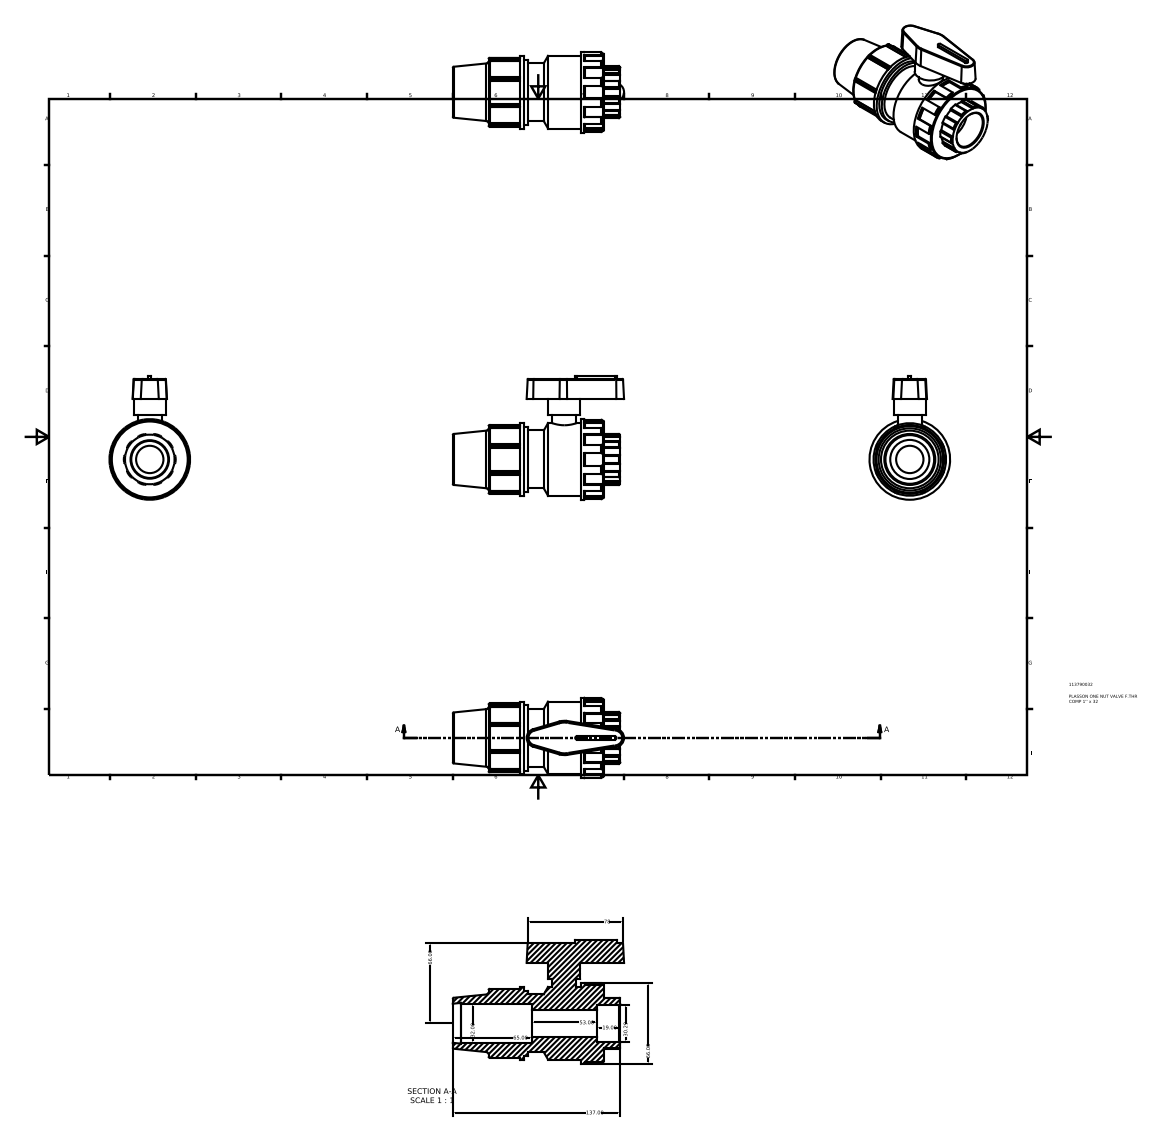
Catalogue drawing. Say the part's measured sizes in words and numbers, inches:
The part is named "113790032". Its 3-D file was written by "Autodesk Inventor 2015 (AUTOMOTIVE_DESIGN)". It is 1 solid with 248 faces: 99 planar, 74 cylindrical and 75 other. Overall it measures 5.52 by 3.976 by 2.598 inches. Its volume is 15.87 cubic inches and its surface area 77.58 square inches. Round holes: 1 of diameter 0.882, 1 of diameter 1.193, 1 of diameter 1.26. Round bosses or shafts: 1 of diameter 2.598, 1 of diameter 2.494, 1 of diameter 2.339, 1 of diameter 2.222, 1 of diameter 2.105, 1 of diameter 1.871, 1 of diameter 1.039, 1 of diameter 0.78. Partial cylindrical surfaces (rounded edges, fillets, slot ends): 20 of radius 0.036, 16 of radius 0.038, 4 of radius 0.024, 2 of radius 0.052, 1 of radius 0.799, 1 of radius 0.835. The main face-to-face distances are 0.65, 0.748, 0.524, 1.152, 1.819, 2.567, 3.091, 1.272, 0.117, 1.702.
